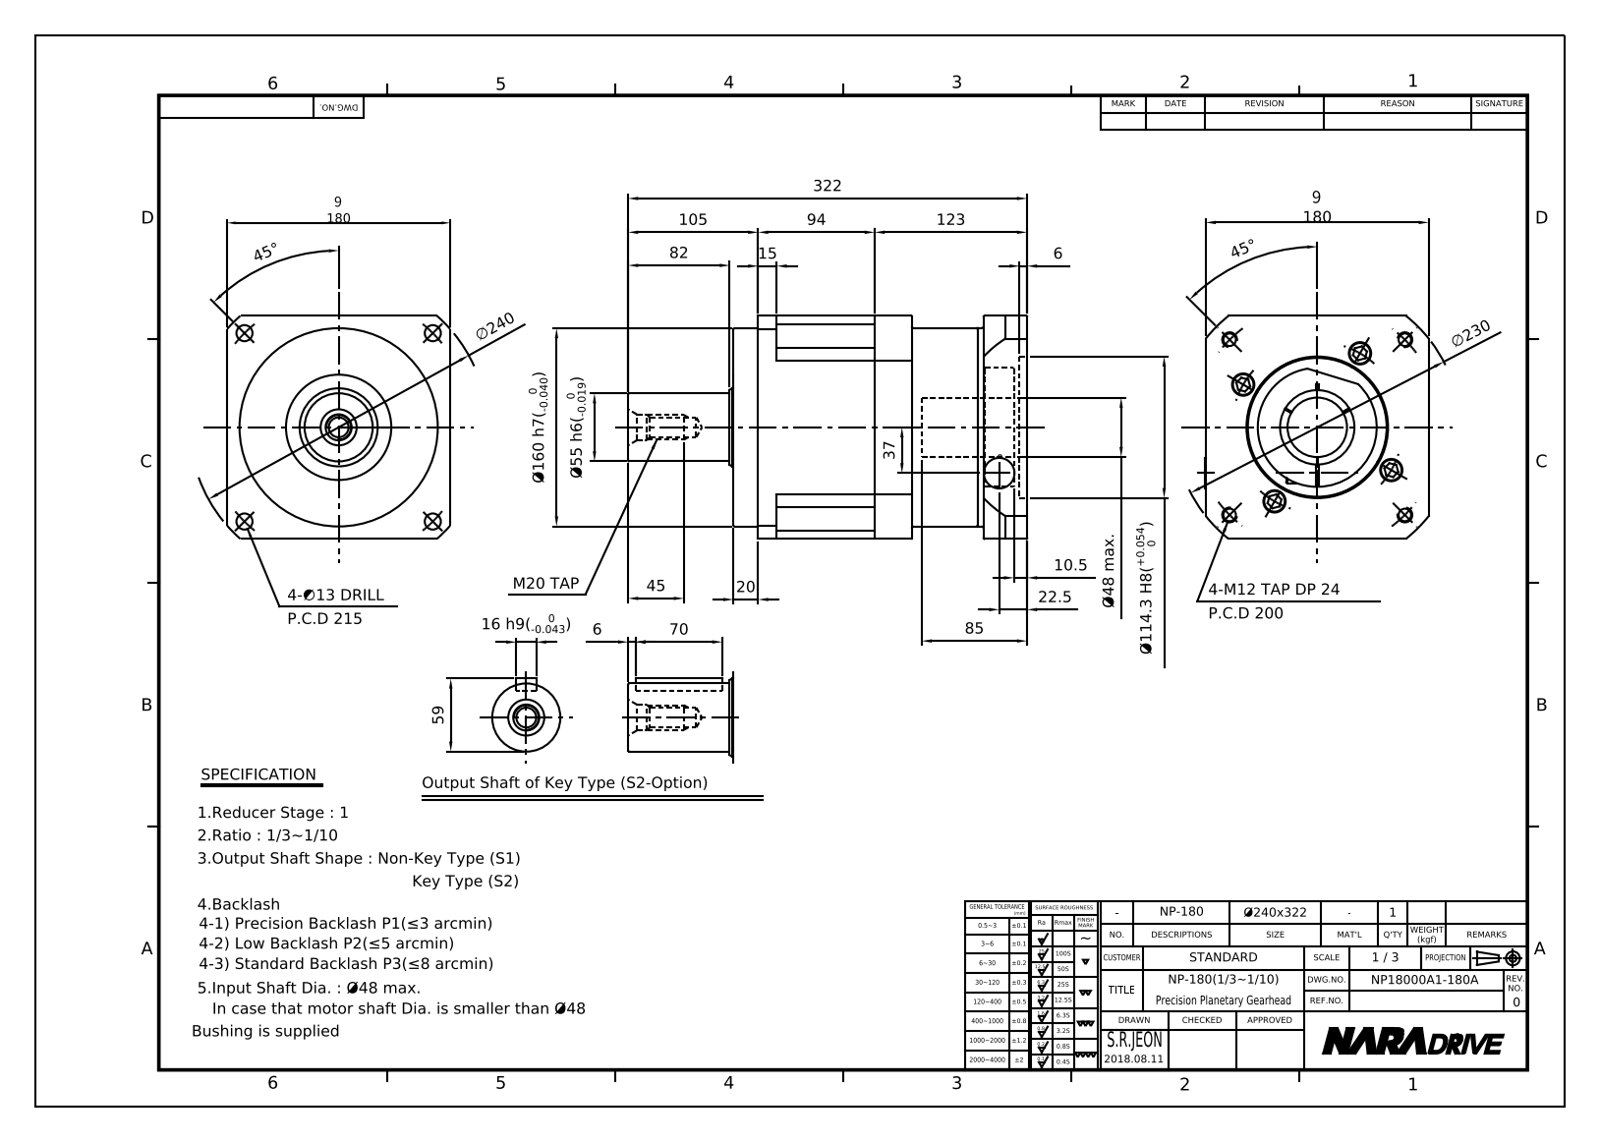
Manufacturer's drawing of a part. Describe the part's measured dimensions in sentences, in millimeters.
The part is named "NP18000A1-180A-S1". Its 3-D file was written by "Autodesk Inventor 2015 (AUTOMOTIVE_DESIGN)". It is 2 solids with 418 faces: 196 planar, 117 cylindrical and 105 other. Overall it measures 322 by 182.03 by 181.33 millimeters. Its volume is 5 183 000 cubic millimeters and its surface area 401 261 square millimeters. Round holes: 8 of diameter 10.11, 5 of diameter 8.38, 5 of diameter 11, 4 of diameter 13, 4 of diameter 14, 4 of diameter 17.5, 4 of diameter 20, 1 of diameter 12.5, 1 of diameter 14.5, 1 of diameter 17.29, 1 of diameter 21, 1 of diameter 35. Round bosses or shafts: 5 of diameter 16, 5 of diameter 10, 4 of diameter 18, 4 of diameter 12, 1 of diameter 160, 1 of diameter 96, 1 of diameter 63, 1 of diameter 55. Partial cylindrical surfaces (rounded edges, fillets, slot ends): 4 of radius 0.5, 4 of radius 2, 4 of radius 15, 1 of radius 9, 1 of radius 105, 1 of radius 115, 1 of radius 120. The main face-to-face distances are 101, 136, 180.08, 237, 180.09, 13, 180.01, 217, 88, 20. The hole center spacings are 146.83, 26.2, 117.34, 130.82, 135.4, 140.36, 141.43, 152.79.
